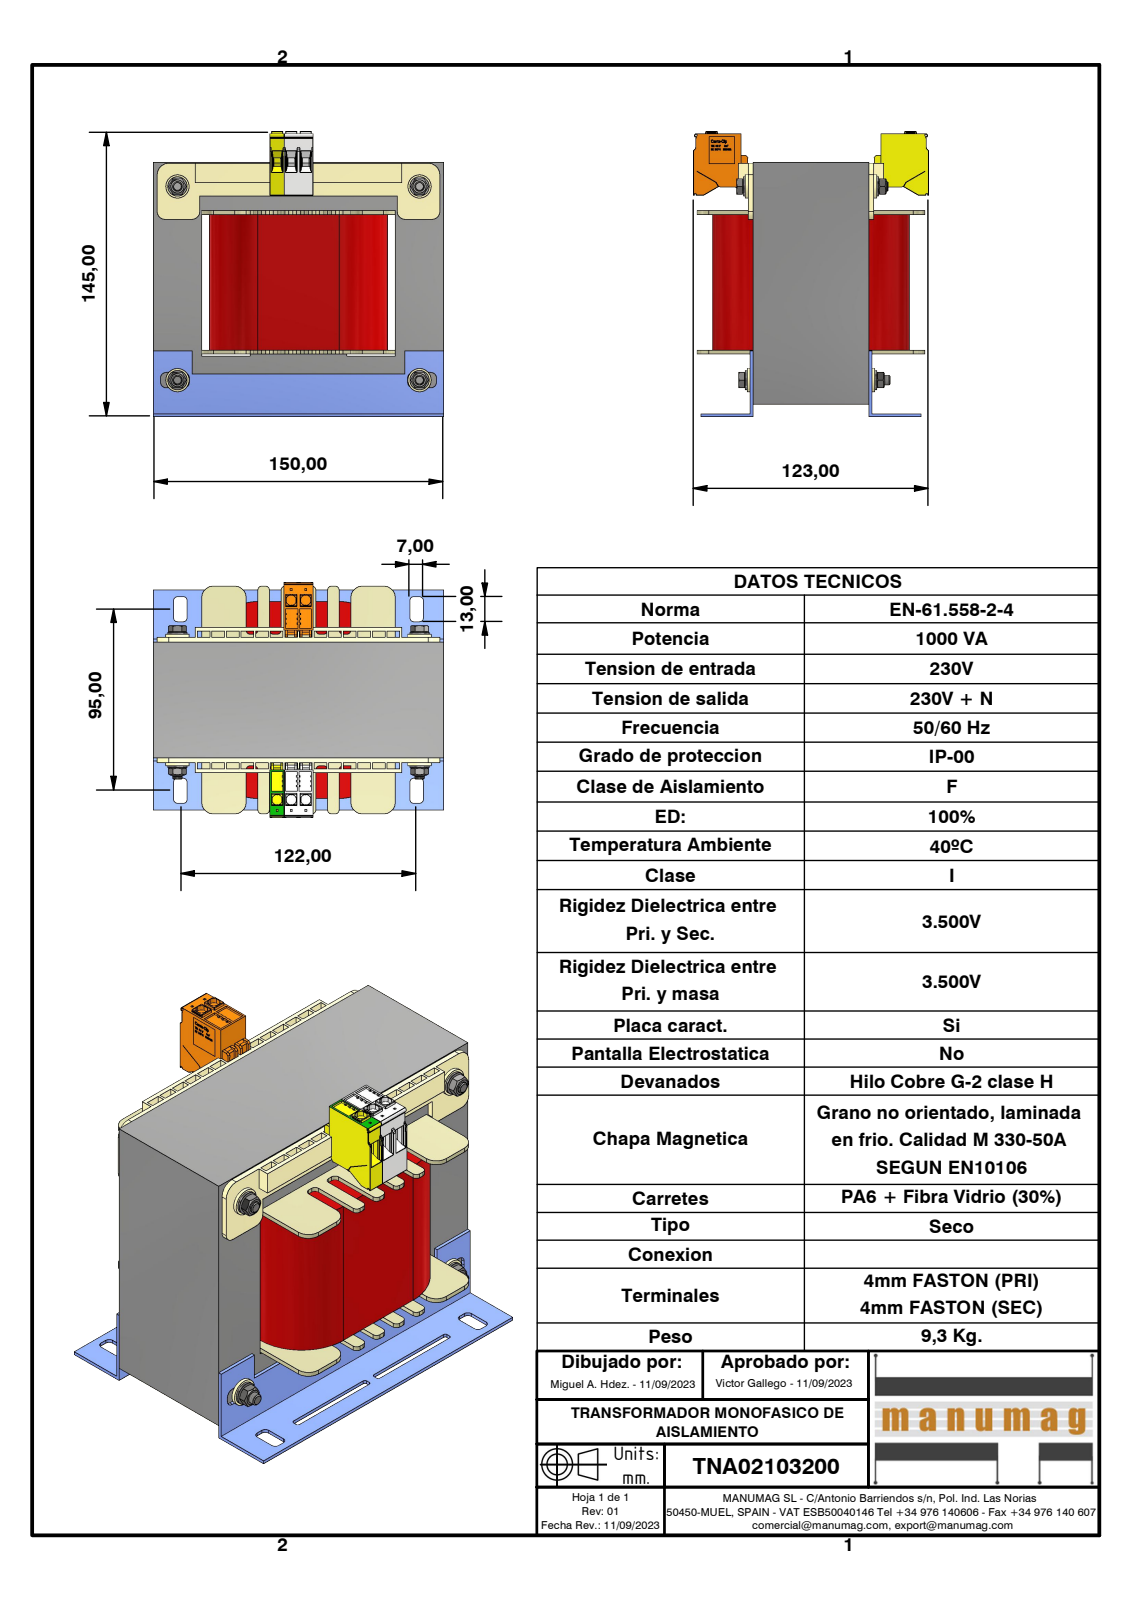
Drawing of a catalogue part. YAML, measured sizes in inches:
part_name: "TNA02103200; EI150 x 125 - 60 (RC50); AF50DIN; EI150 (+8 more)"
step_written_by: "Autodesk Inventor 2023 (AUTOMOTIVE_DESIGN)"
units: inches
bodies: {solids: 33, faces: 5367, planar: 4383, cylindrical: 680, other: 304}
overall_size: [5.906, 5.803, 4.799]
volume: 85.22
surface_area: 365.3
round_holes:
  - {diameter: 0.163, count: 4}
  - {diameter: 0.197, count: 4}
  - {diameter: 0.209, count: 4}
  - {diameter: 0.315, count: 4}
round_bosses_or_shafts:
  - {diameter: 0.472, count: 4}
  - {diameter: 0.394, count: 4}
  - {diameter: 0.264, count: 4}
  - {diameter: 0.232, count: 4}
  - {diameter: 0.18, count: 4}
partial_cylinders:
  - {radius: 0.006, count: 216}
  - {radius: 0.008, count: 70}
  - {radius: 0.079, count: 51}
  - {radius: 0.039, count: 24}
  - {radius: 0.02, count: 18}
  - {radius: 0.012, count: 12}
  - {radius: 0.236, count: 10}
  - {radius: 0.118, count: 8}
face_to_face_distances: [3.937, 0.984, 2.362, 1.969, 4.921, 0.059, 0.827, 2.953, 0.039, 0.079]
hole_center_spacings: [3.937, 4.921, 6.302]
